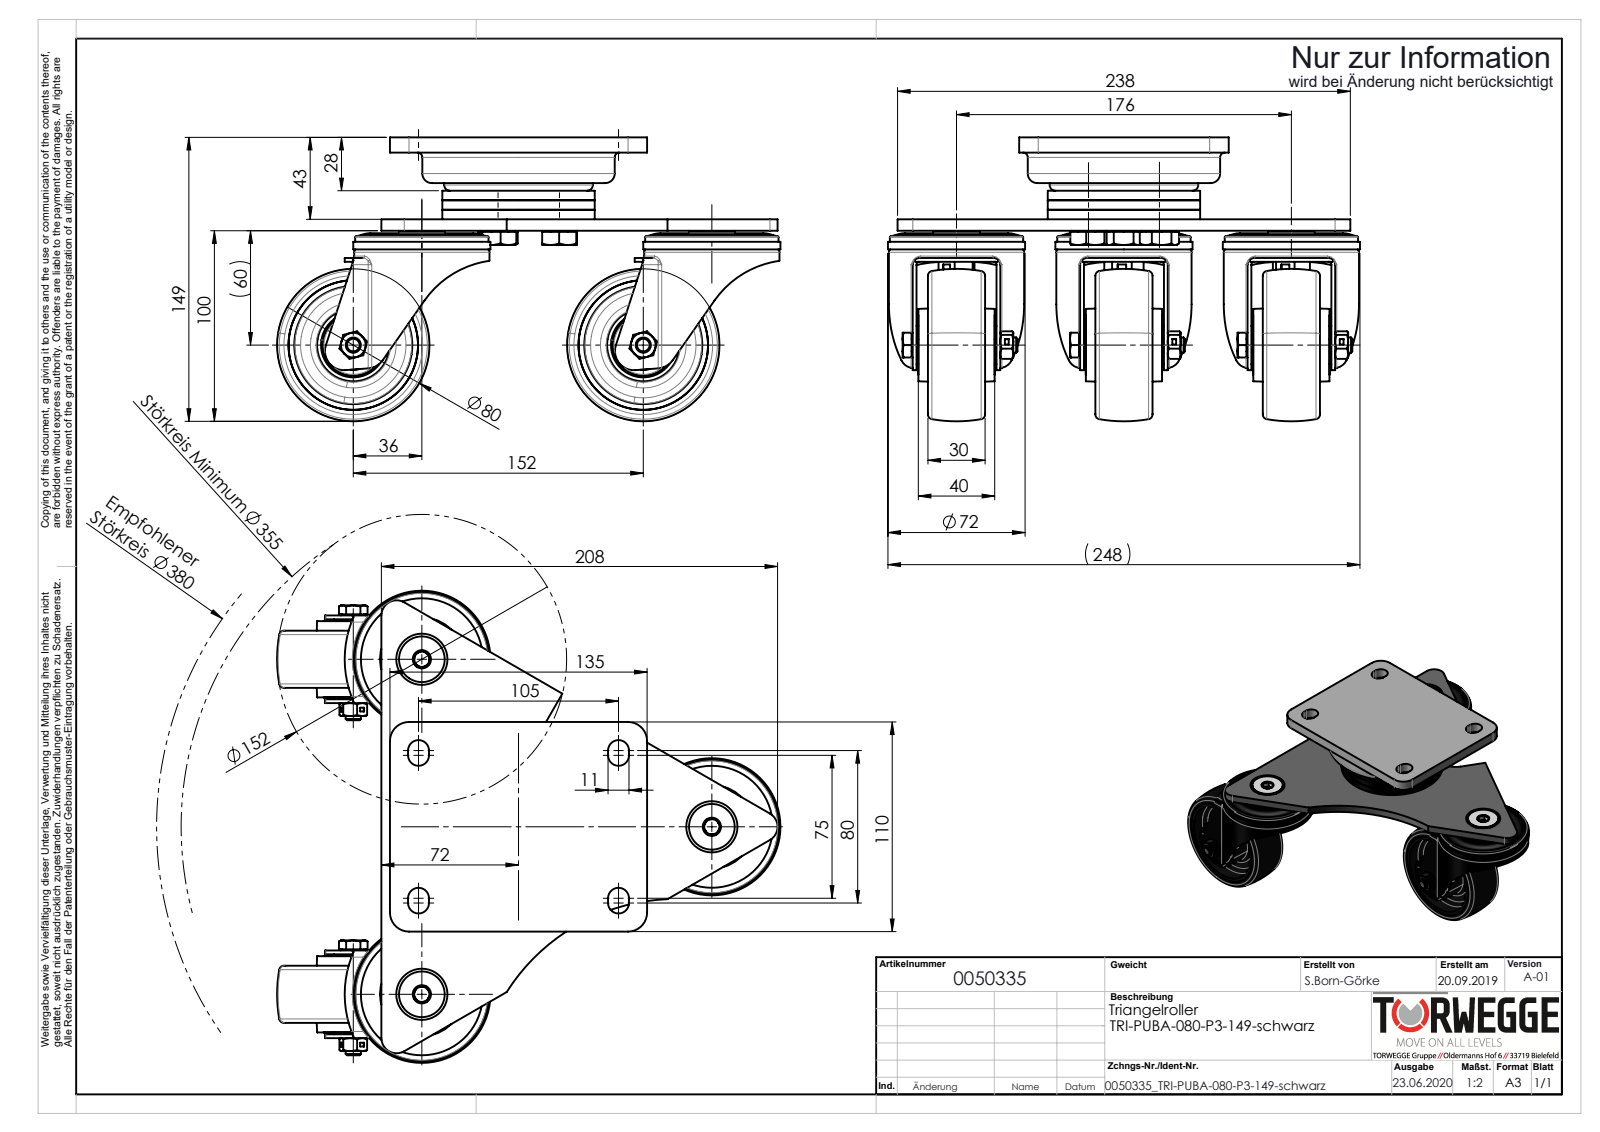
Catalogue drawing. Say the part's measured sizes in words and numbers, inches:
The part is named "0050335". Its 3-D file was written by "SolidWorks 2018 (AUTOMOTIVE_DESIGN)". It is 74 solids with 1451 faces: 493 planar, 451 cylindrical and 507 other. Overall it measures 10.404 by 9.756 by 5.866 inches. Its volume is 58.77 cubic inches and its surface area 654.6 square inches. Round holes: 7 of diameter 0.472, 6 of diameter 0.402, 3 of diameter 0.492, 3 of diameter 0.512, 3 of diameter 0.551, 3 of diameter 2.638, 2 of diameter 0.268, 2 of diameter 0.315, 2 of diameter 0.323, 2 of diameter 0.488, 2 of diameter 1.024, 2 of diameter 1.142. Round bosses or shafts: 5 of diameter 0.709, 3 of diameter 2.835, 3 of diameter 2.795, 3 of diameter 2.756, 3 of diameter 0.945, 2 of diameter 1.26, 2 of diameter 0.787, 2 of diameter 0.591. Partial cylindrical surfaces (rounded edges, fillets, slot ends): 8 of radius 0.217, 8 of radius 0.394, 6 of radius 0.059, 6 of radius 0.098, 6 of radius 0.138, 6 of radius 0.177, 3 of radius 0.197, 3 of radius 0.315. The main face-to-face distances are 0.236, 0.197, 0.602, 0.366, 0.394, 0.079, 1.496, 2.295, 1.929, 1.693. The hole center spacings are 4.48, 1.466, 3.15, 6.921, 5.994.
